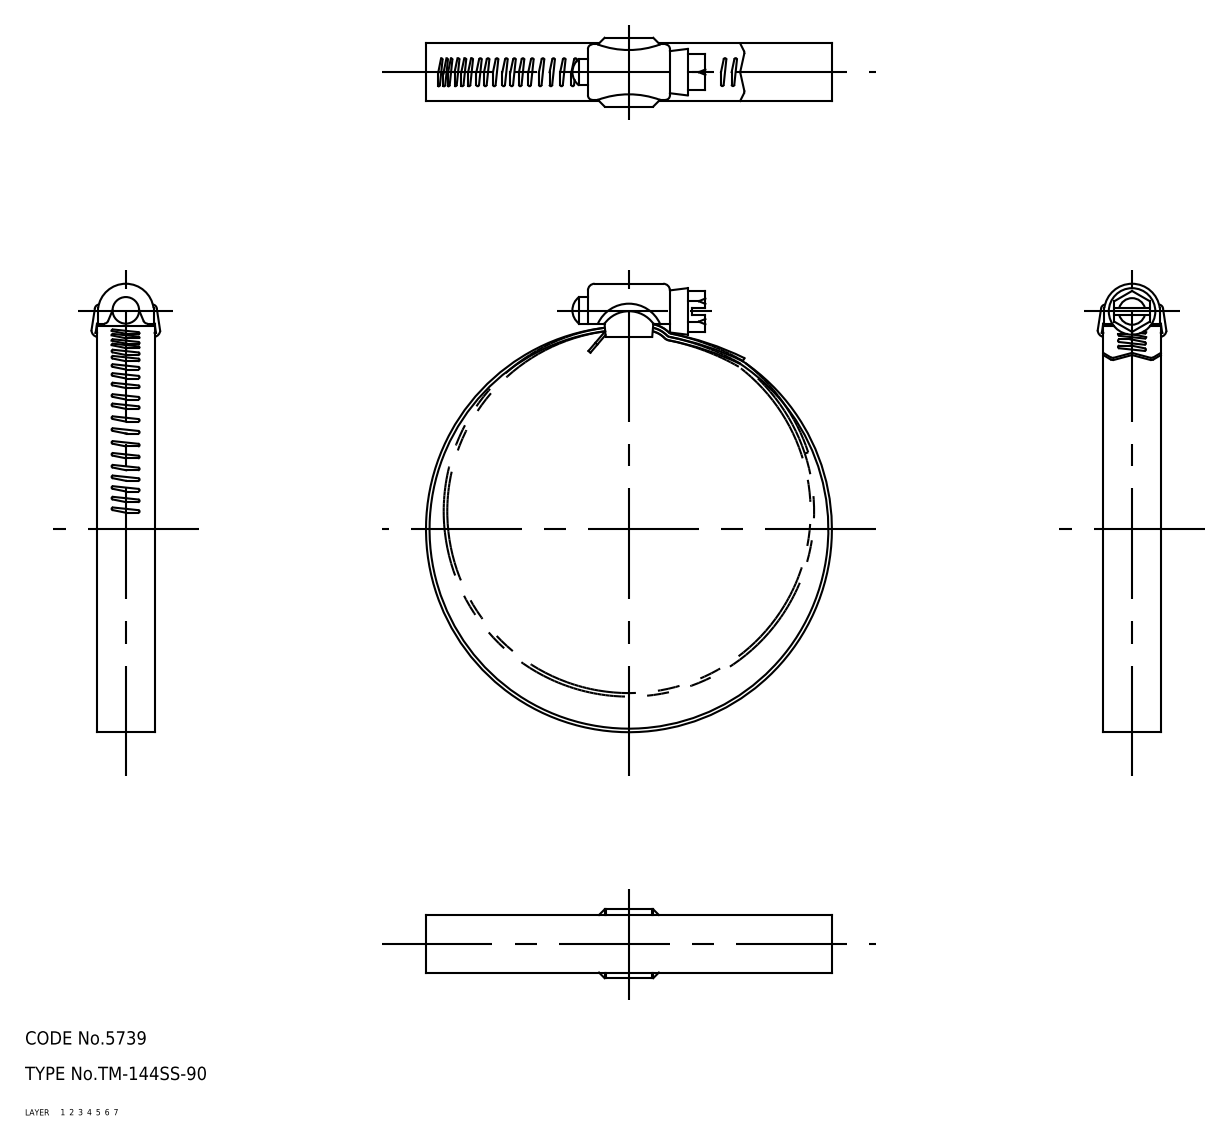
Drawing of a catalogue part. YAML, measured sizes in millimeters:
part_name: "screw; holder; band; TM_144SS_90_20237_36"
step_written_by: "CADfix (AUTOMOTIVE_DESIGN)"
units: millimeters
bodies: {solids: 3, faces: 215, planar: 0, cylindrical: 0, other: 215}
overall_size: [101.21, 91.6, 15.63]
volume: 5457
surface_area: 11120
